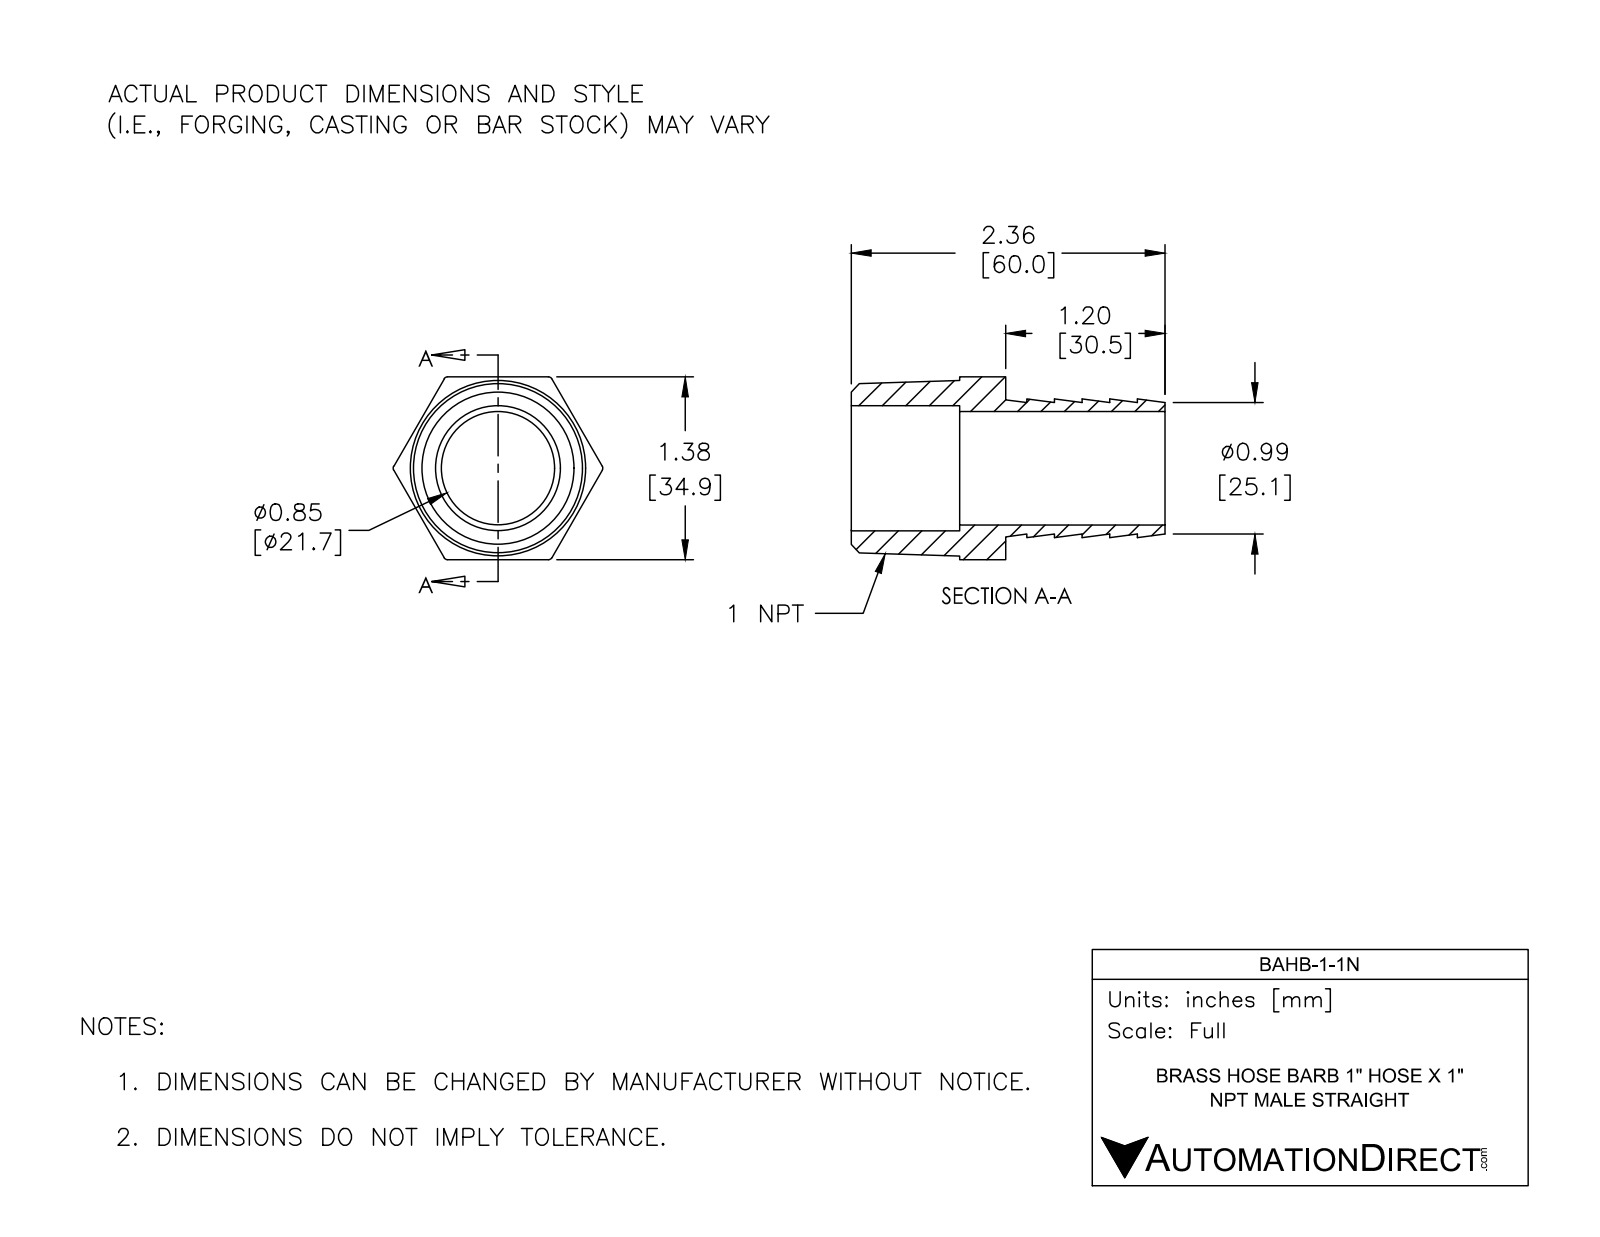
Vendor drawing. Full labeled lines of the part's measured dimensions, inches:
Part name (STEP PRODUCT): BAHB-1-1N
STEP written by: SolidWorks 2017 (AUTOMOTIVE_DESIGN)
Units: inches
Bodies: 1 solid, 42 faces (16 planar, 10 cylindrical, 16 other)
Overall size (bounding box): 2.361 × 1.578 × 1.375
Volume: 1.155 in³ · Surface area: 17.62 in²
Round holes (diameter × count): ⌀0.853 ×1, ⌀0.941 ×1
Partial cylindrical surfaces — rounded edges, fillets, slot ends (radius × count): R0.03 ×6
Main face-to-face distances: 1.375, 0.346, 1.162, 0.816, 0.208, 0.416, 0.624, 1.199, 1.545, 2.361
